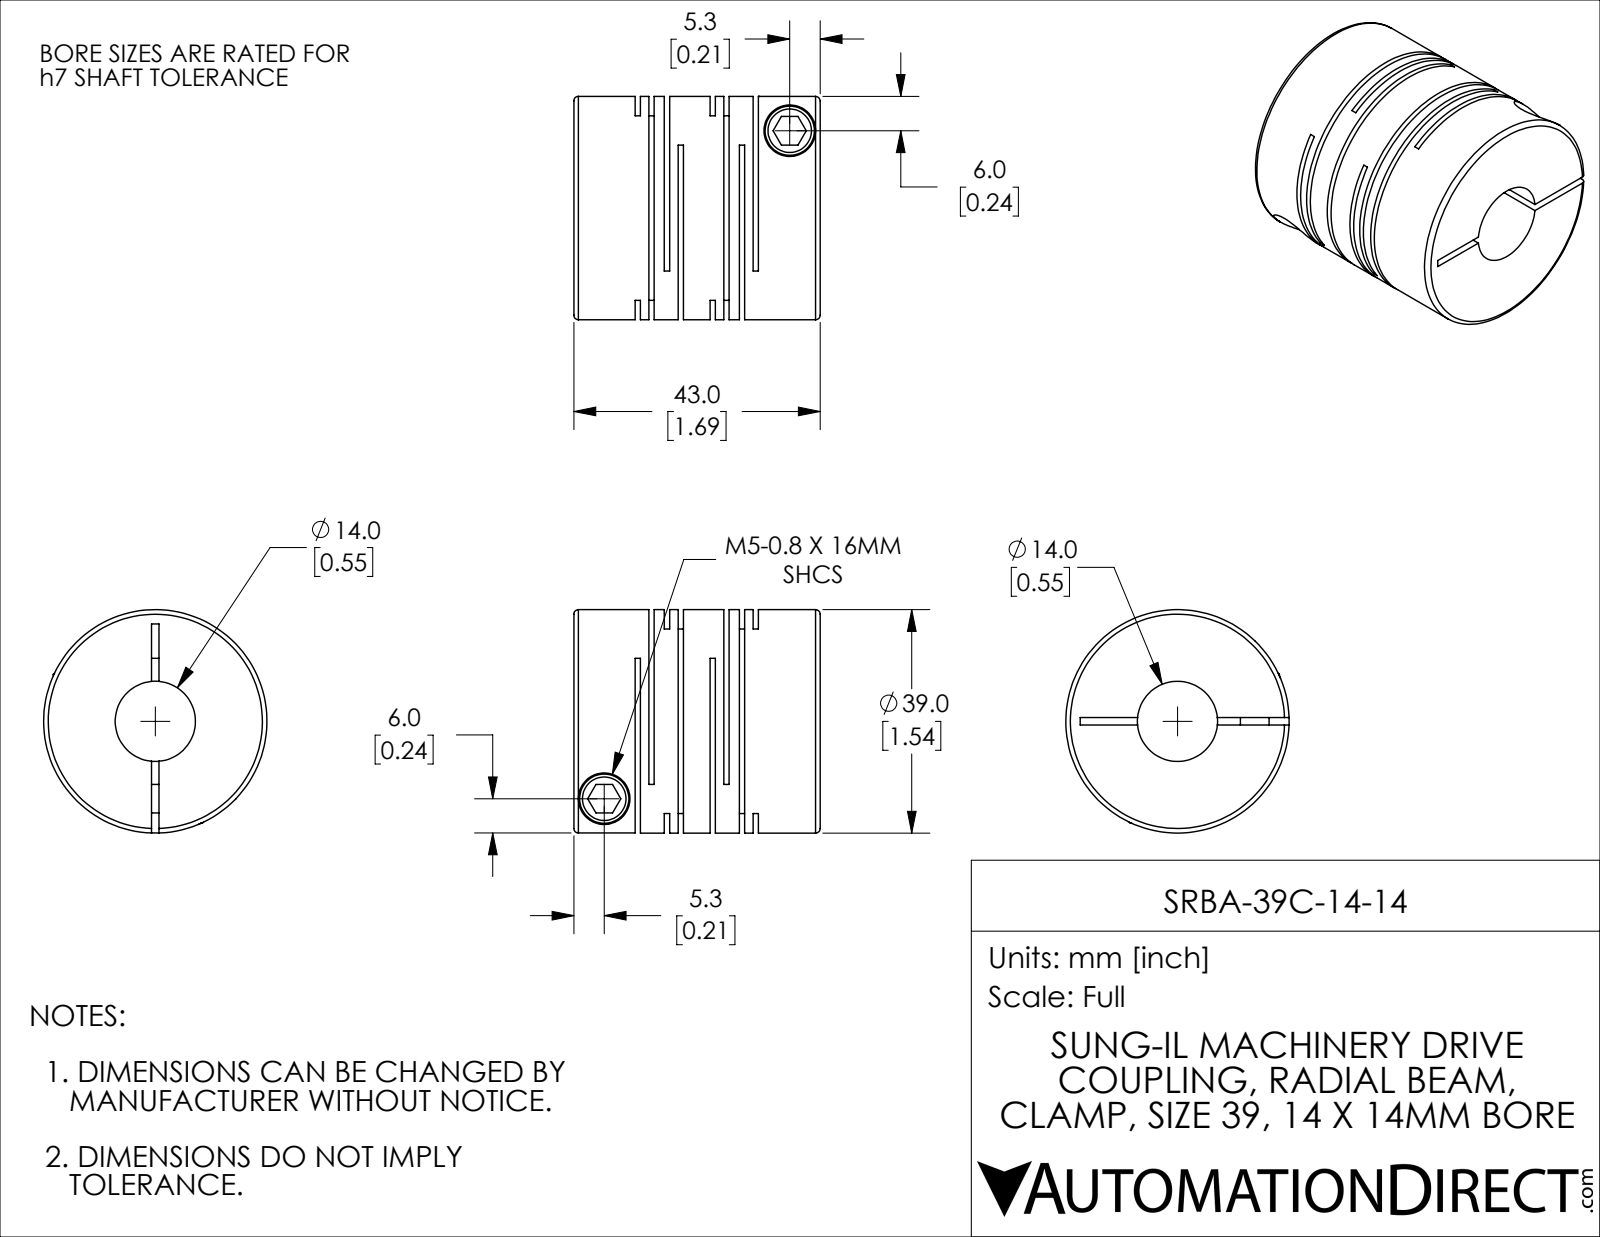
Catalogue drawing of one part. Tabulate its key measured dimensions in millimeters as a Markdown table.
| quantity | value |
| --- | --- |
| part name | SRBA-39C-14-14 |
| STEP written by | SolidWorks 2021 (CONFIG_CONTROL_DESIGN) |
| units | millimeters |
| bodies | 1 solid, 114 faces (60 planar, 42 cylindrical, 12 other) |
| overall size | 43 × 39 × 39 |
| volume | 36 967 mm³ |
| surface area | 23 649 mm² |
| round holes (diameter × count) | 5 × 2, 9 × 2, 14 × 1 |
| round bosses / shafts (diameter × count) | 8.6 × 2, 39 × 1 |
| main face-to-face distances | 13.1, 0.92, 2.4, 5.1, 10.7, 14.02, 18.2, 1.48, 12.18, 4.18 |
